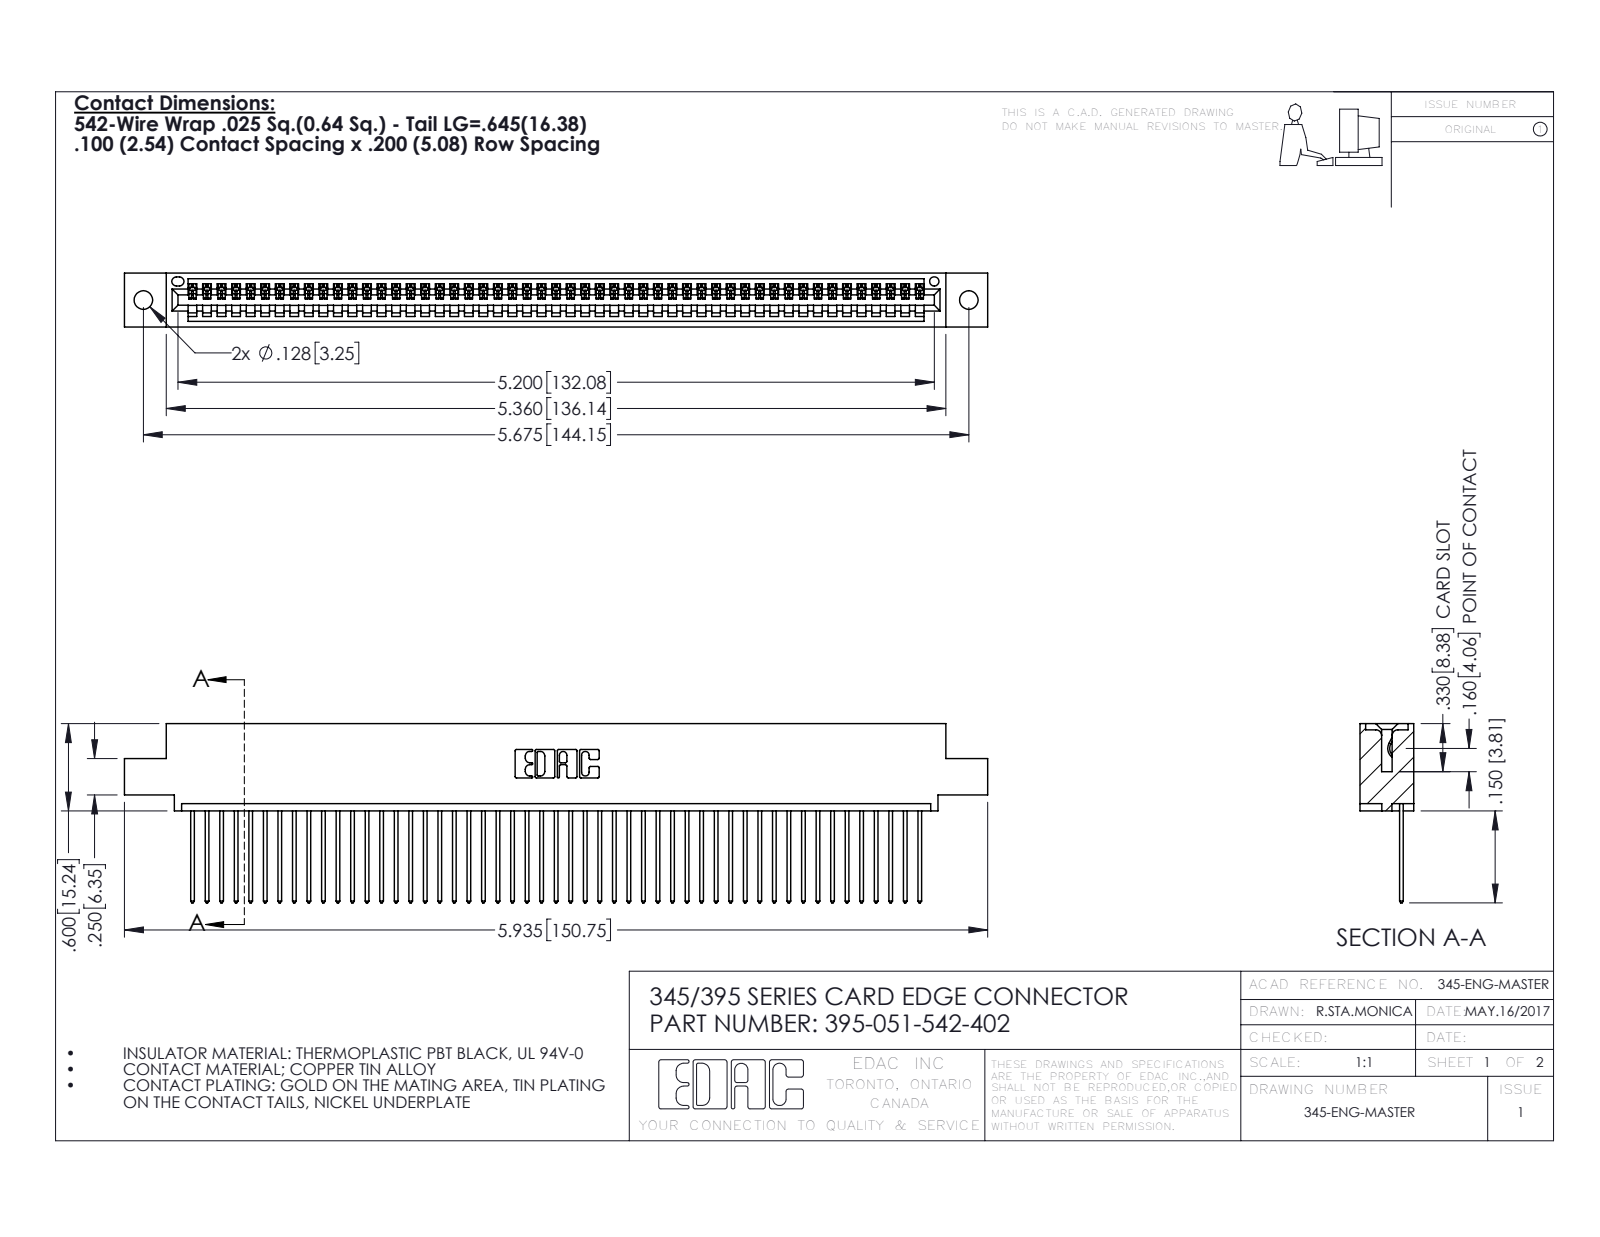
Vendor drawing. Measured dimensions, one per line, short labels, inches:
name: 395-051-542-402; 345-292-001_345-293-142; 345 Part_0.110 Offset - 0.128 Dia
written by: SolidWorks 2016 (CONFIG_CONTROL_DESIGN)
unit: in
bodies: 52 solids, 3088 faces (2124 planar, 964 cylindrical, 0 other)
size: 5.935 × 1.232 × 0.37
volume: 0.878 in³; area: 30.66 in²
holes: 2× ⌀0.128, 1× ⌀0.064
rounds: 102× R0.006, 102× R0.01, 22× R0.01, 6× R0.007, 6× R0.031, 3× R0.026, 2× R0.031, 2× R0.04
face distances: 0.072, 0.298, 0.098, 0.272, 0.025, 0.37, 0.2, 0.225, 0.149, 0.072
hole spacings: 0.27, 5.439, 5.675
